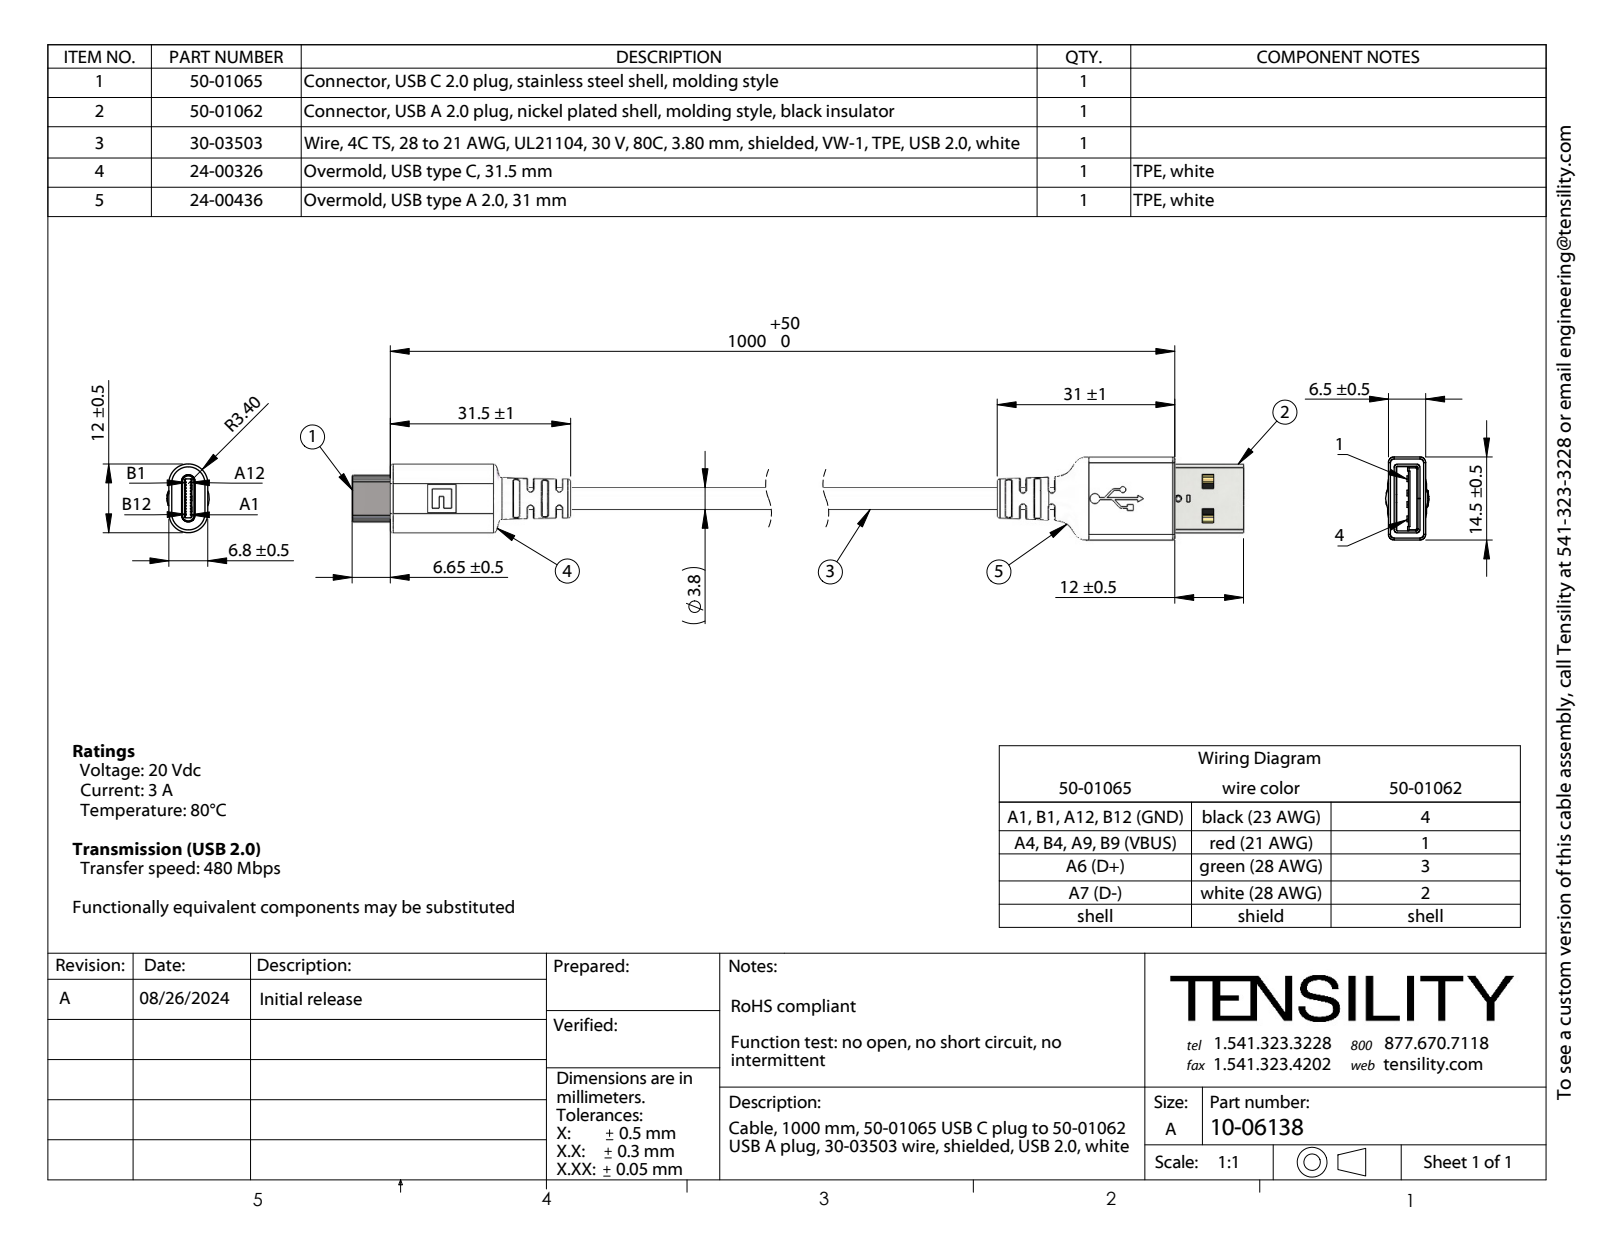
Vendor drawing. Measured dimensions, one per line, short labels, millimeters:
name: 50-01065_Hidden emarker; 50-01062_insulator_model; 50-01062_pin1; 50-01062_Assembled (+8 more)
written by: SolidWorks 2021 (CONFIG_CONTROL_DESIGN)
unit: mm
bodies: 125 solids, 1970 faces (1014 planar, 630 cylindrical, 326 other)
size: 211.15 × 14.5 × 7.54
volume: 5 918 mm³; area: 22 580 mm²
holes: 1× ⌀1.04, 1× ⌀1.74, 1× ⌀2.61, 1× ⌀2.64, 1× ⌀2.84
bosses: 2× ⌀0.83, 1× ⌀3.8, 1× ⌀2.63, 1× ⌀1.2, 1× ⌀1
rounds: 40× R0.25, 34× R0.2, 32× R0.5, 14× R0.35, 14× R0.4, 13× R0.3, 5× R0.31, 5× R0.6
face distances: 0.35, 4.15, 1, 5.5, 1.35, 5.15, 1.5, 2.5, 4.5, 3.8
hole spacings: 5.12
